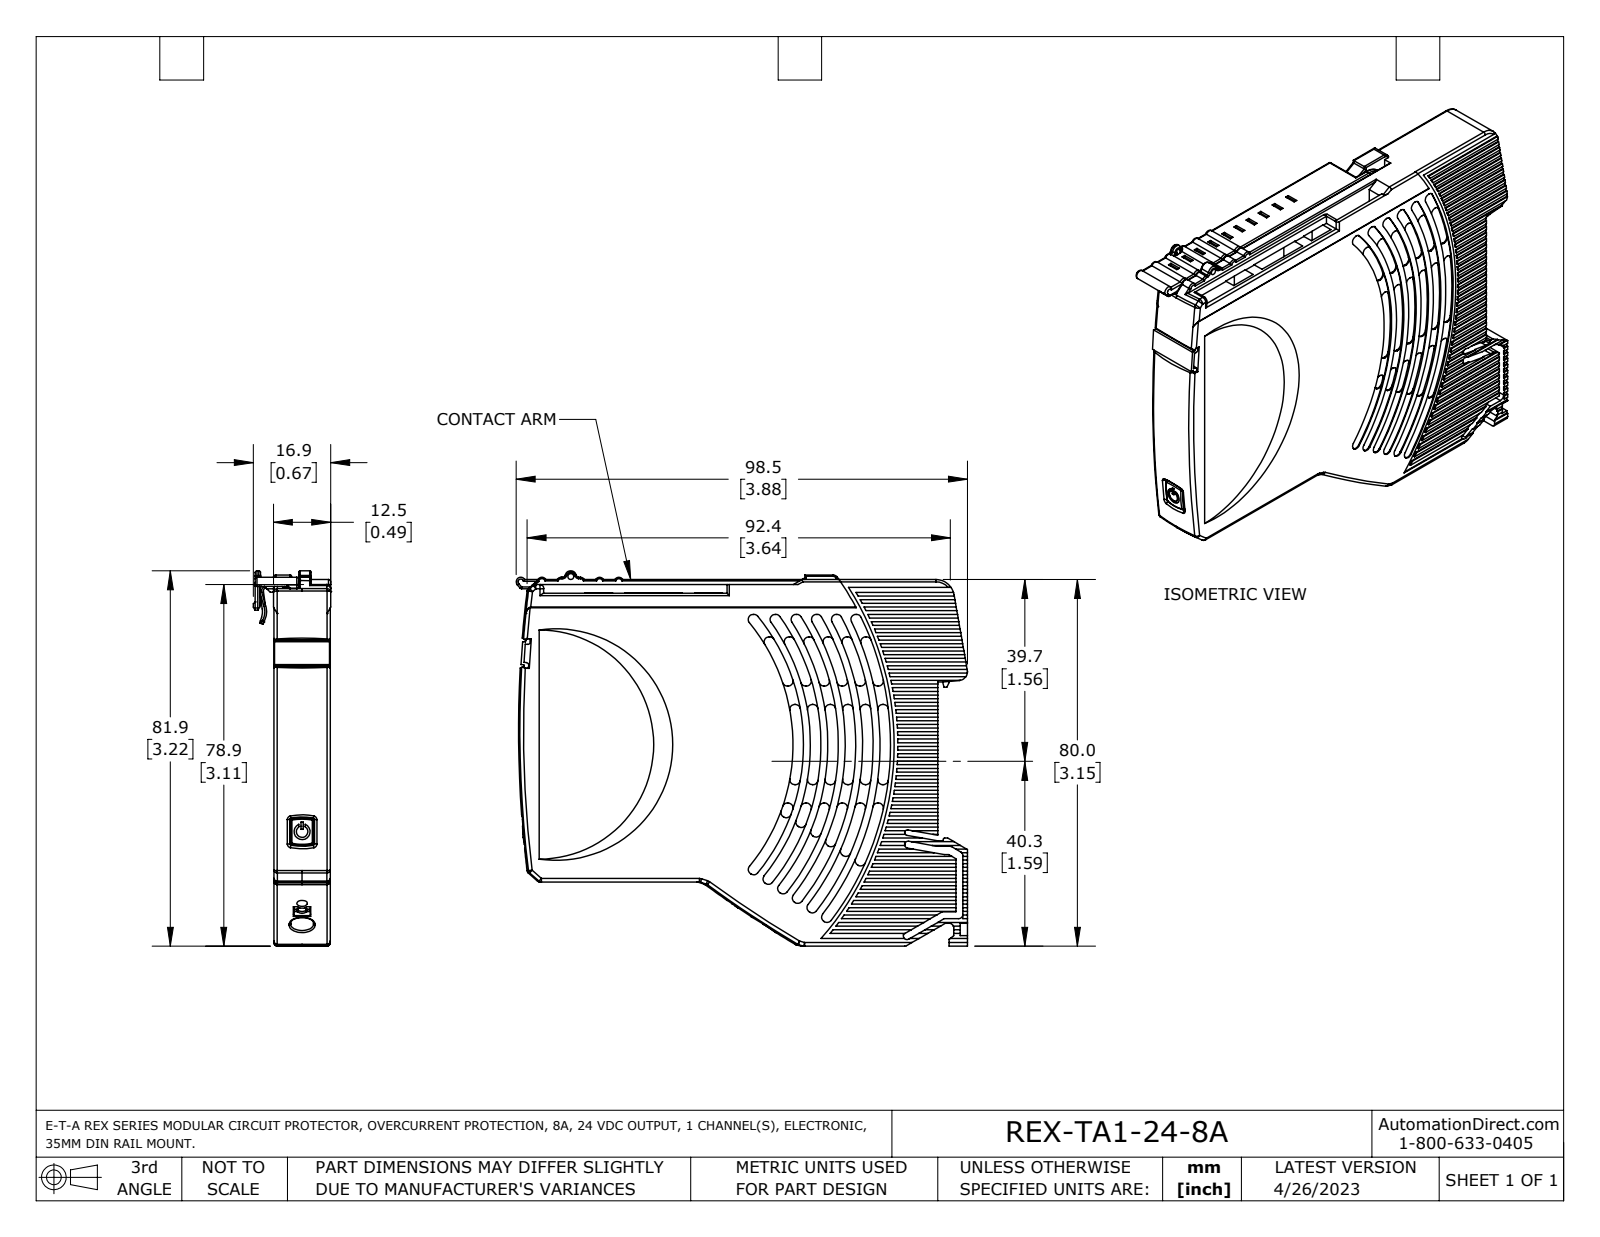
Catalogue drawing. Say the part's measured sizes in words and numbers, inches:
The part is named "t-rex12-ta1-1xx_asm_ik01". Its 3-D file was written by "SolidWorks 2021 (AUTOMOTIVE_DESIGN)". It is 2 solids with 1842 faces: 1044 planar, 613 cylindrical and 185 other. Overall it measures 3.878 by 3.224 by 0.665 inches. Its volume is 4.809 cubic inches and its surface area 40.68 square inches. Round holes: 1 of diameter 0.051, 1 of diameter 0.091, 1 of diameter 0.138, 1 of diameter 0.161. Round bosses or shafts: 1 of diameter 0.157, 1 of diameter 0.098, 1 of diameter 0.079. Partial cylindrical surfaces (rounded edges, fillets, slot ends): 98 of radius 0.043, 61 of radius 0.02, 27 of radius 0.016, 25 of radius 0.039, 18 of radius 0.012, 17 of radius 0.031, 12 of radius 0.008, 6 of radius 0.03. The main face-to-face distances are 0.484, 0.476, 0.469, 0.016, 0.461, 0.059, 0.02, 0.453, 0.256, 0.039. The hole center spacings are 2.024.
